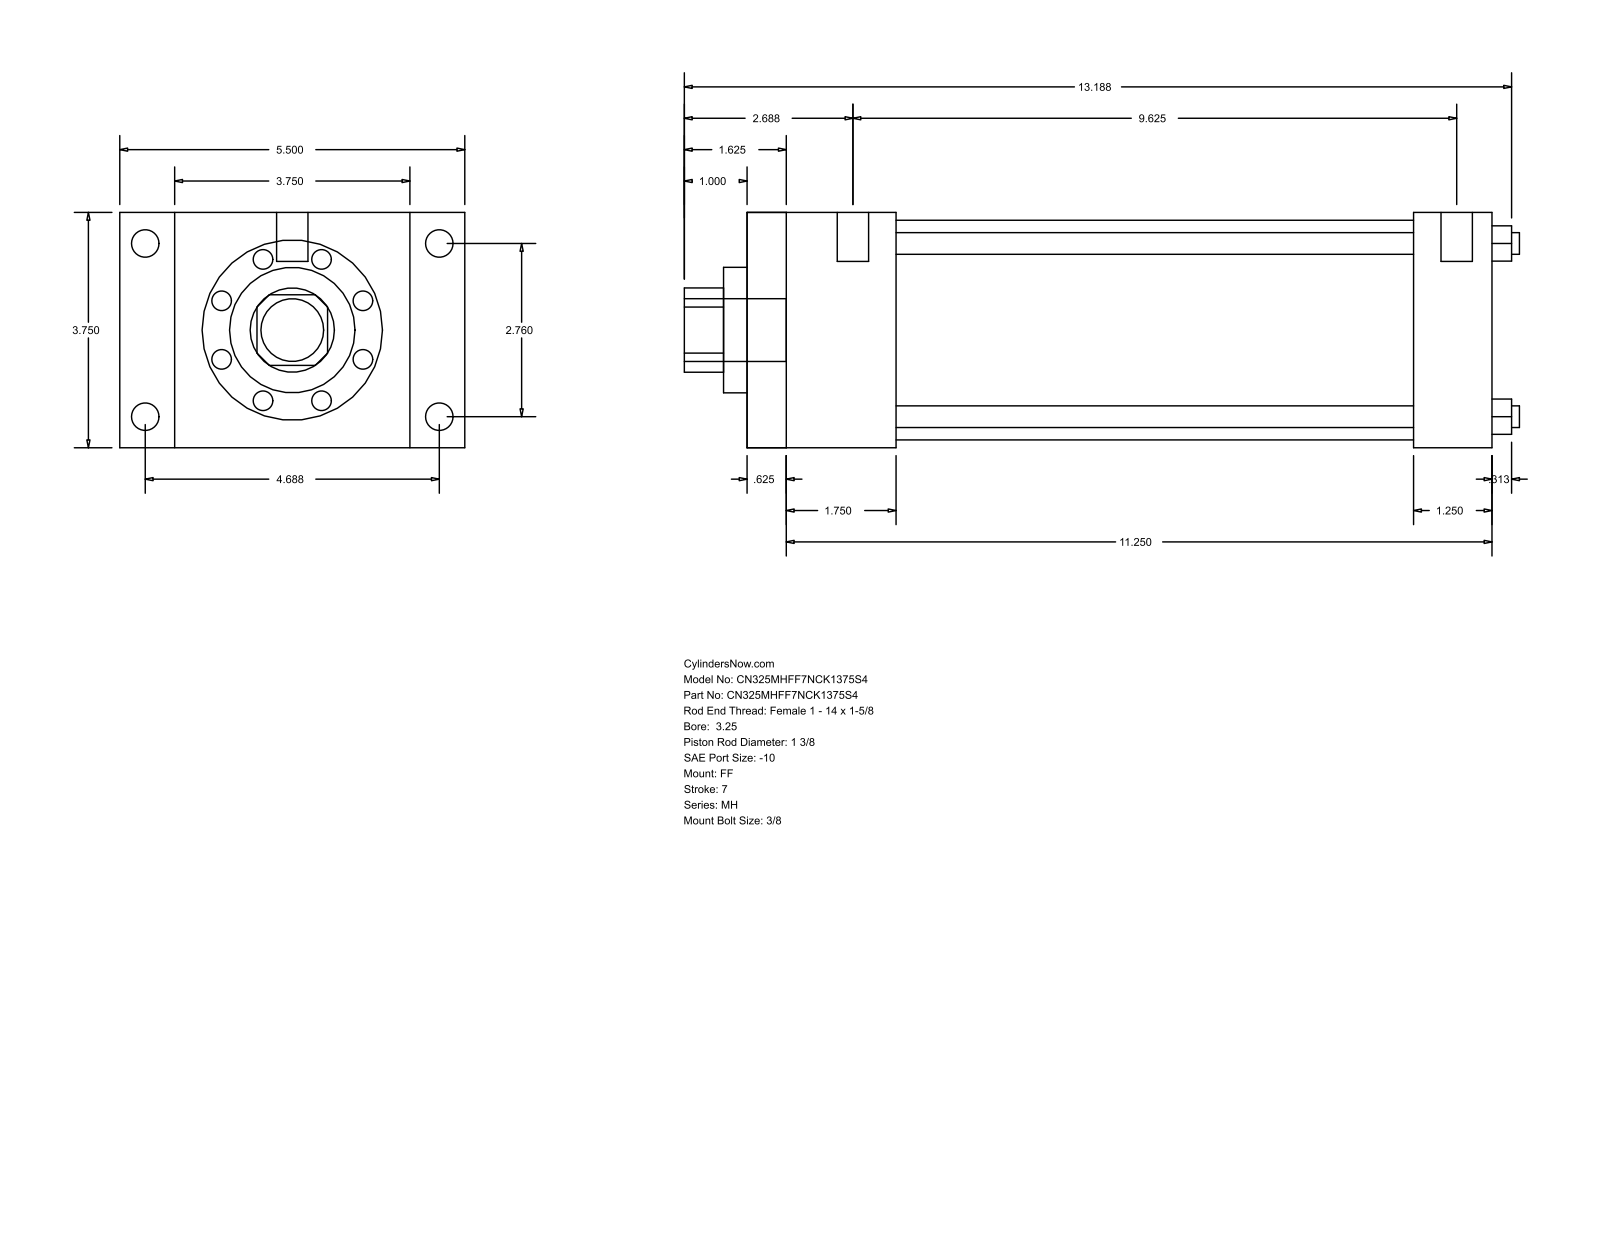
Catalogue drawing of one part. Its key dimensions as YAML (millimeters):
part_name: "MH_FF__0325_1.375"
step_written_by: "GSSL Pune (CONFIG_CONTROL_DESIGN)"
units: millimeters
bodies: {solids: 0, faces: 92, planar: 64, cylindrical: 28, other: 0}
overall_size: [338.14, 139.7, 95.25]
round_holes:
  - {diameter: 8.76, count: 4}
  - {diameter: 34.92, count: 1}
  - {diameter: 50.8, count: 1}
  - {diameter: 88.9, count: 1}
round_bosses_or_shafts:
  - {diameter: 11.13, count: 4}
  - {diameter: 5.56, count: 4}
  - {diameter: 12.7, count: 2}
  - {diameter: 25.4, count: 1}
partial_cylinders:
  - {radius: 17.06, count: 1}
face_to_face_distances: [95.24, 301.62, 15.87, 285.75, 22.23, 117.47, 269.87, 254, 31.75, 60.32]
hole_center_spacings: [49.57, 70.1, 99.14]
